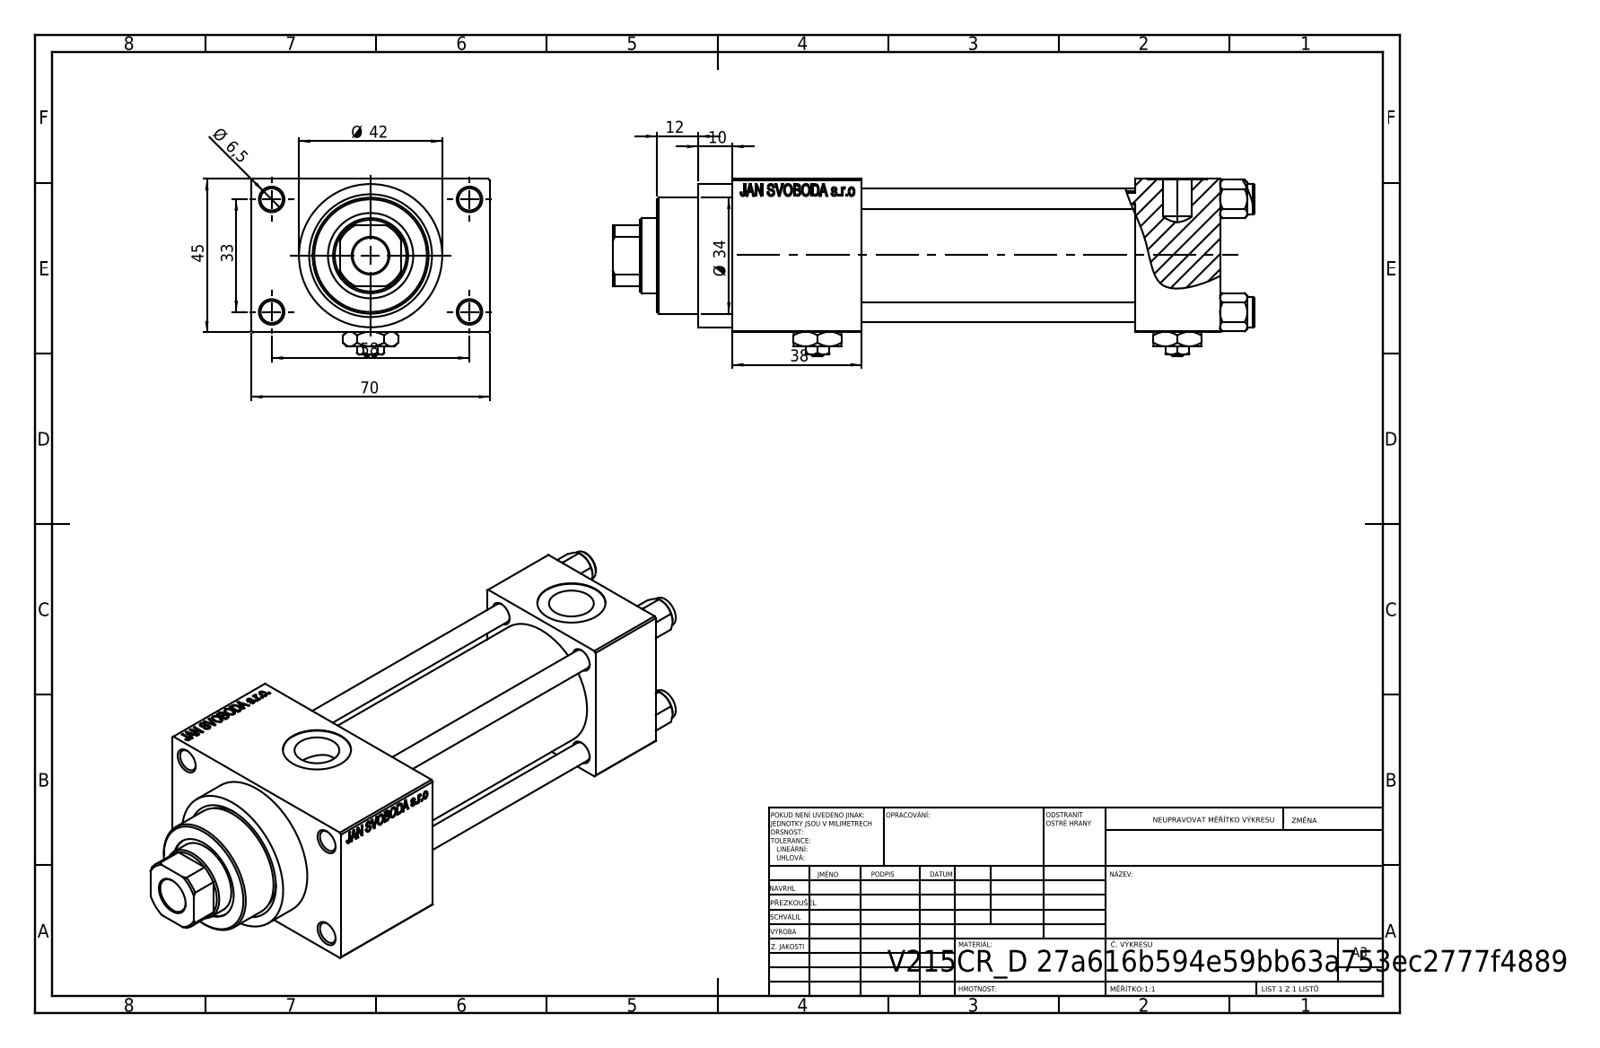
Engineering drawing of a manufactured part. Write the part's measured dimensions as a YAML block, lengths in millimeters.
part_name: "Zatka_pro_OIL_PORT; V215CR_D_TYCINKA; NUT_M5_D; V215_VC_A (+2 more)"
step_written_by: "SolidWorks 2019 (CONFIG_CONTROL_DESIGN)"
units: millimeters
bodies: {solids: 13, faces: 1204, planar: 542, cylindrical: 100, other: 562}
overall_size: [188, 70, 52]
volume: 267940
surface_area: 92045
round_holes:
  - {diameter: 6, count: 4}
  - {diameter: 6.5, count: 4}
  - {diameter: 7, count: 2}
  - {diameter: 13.16, count: 2}
  - {diameter: 20, count: 2}
  - {diameter: 10.5, count: 1}
  - {diameter: 22, count: 1}
  - {diameter: 24, count: 1}
  - {diameter: 25, count: 1}
  - {diameter: 32, count: 1}
  - {diameter: 33, count: 1}
round_bosses_or_shafts:
  - {diameter: 9, count: 4}
  - {diameter: 42, count: 1}
  - {diameter: 38, count: 1}
  - {diameter: 34, count: 1}
partial_cylinders:
  - {radius: 10.5, count: 1}
face_to_face_distances: [45, 25, 12.5, 57.5, 80, 105, 118, 70, 38, 143]
hole_center_spacings: [12.4, 23.48, 33.2, 33.37, 35.35, 45.6, 56.35, 33]
